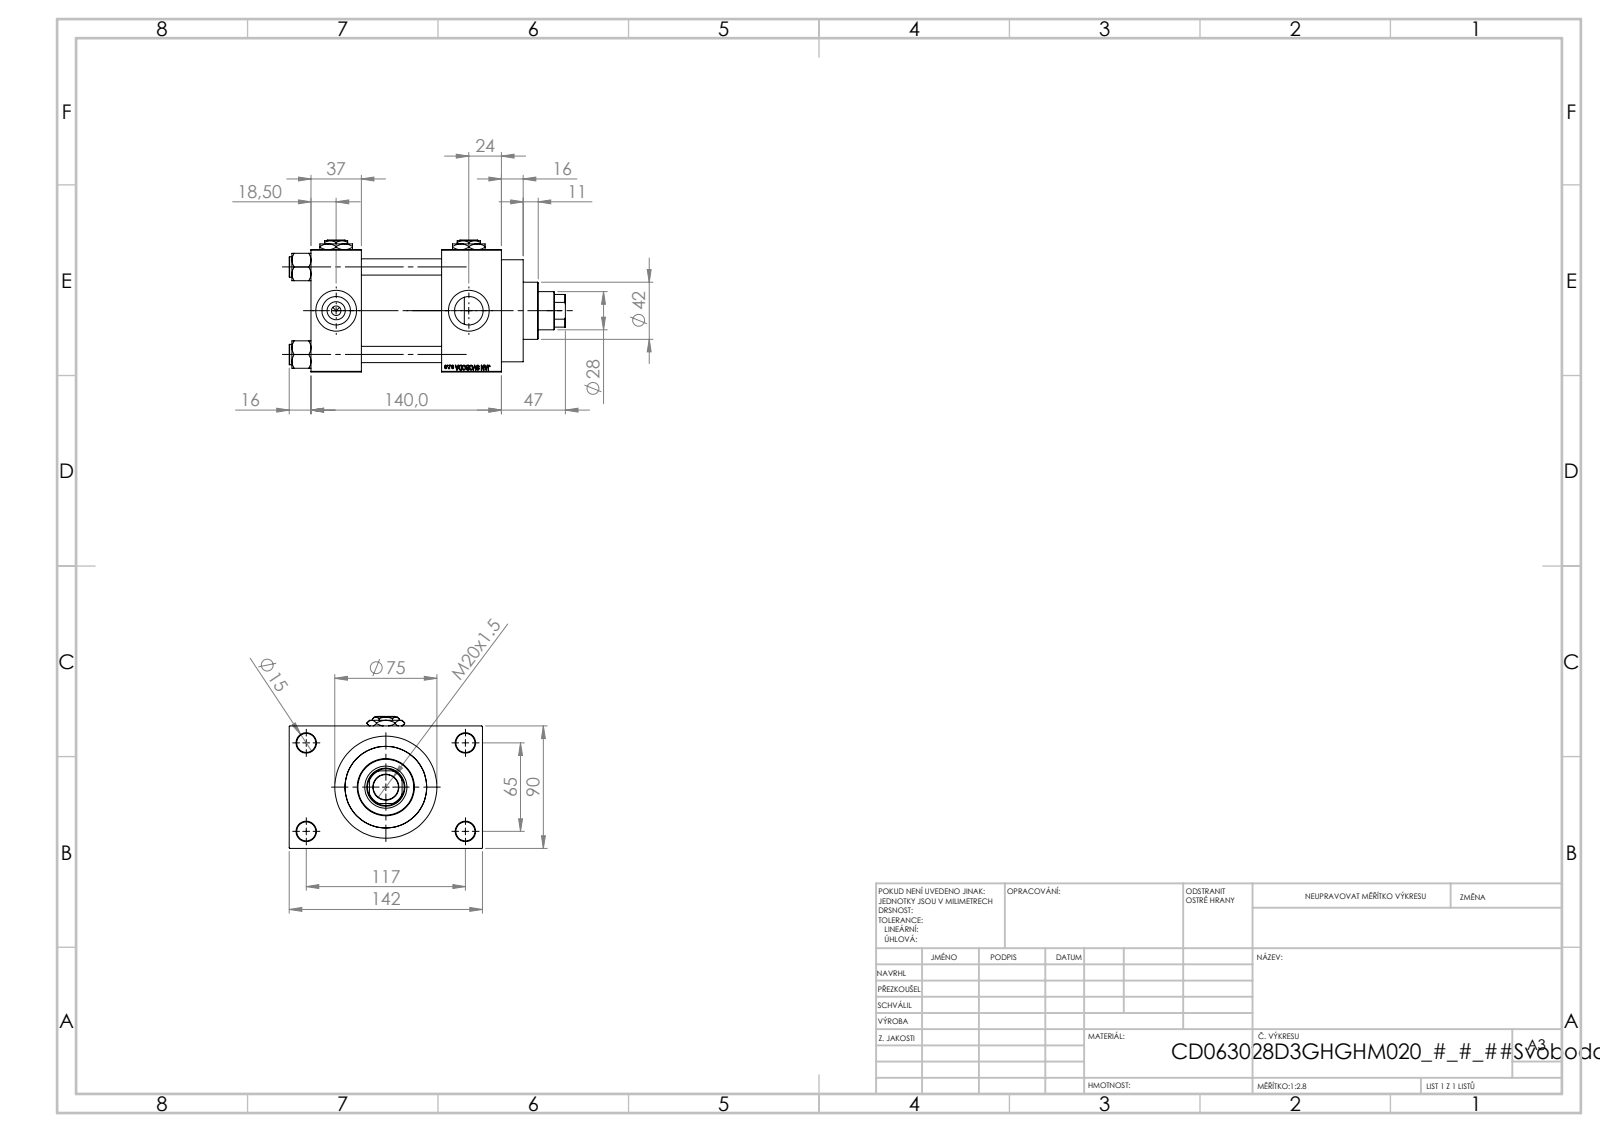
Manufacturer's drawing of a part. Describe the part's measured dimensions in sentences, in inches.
The part is named "V215CD_VC_A; V215CD_D_TYCINKA; Zatka_pro_OIL_PORT; V215CD_NUT_M5_D (+2 more)". Its 3-D file was written by "SolidWorks 2019 (CONFIG_CONTROL_DESIGN)". It is 13 solids with 1204 faces: 545 planar, 99 cylindrical and 560 other. Overall it measures 7.992 by 5.591 by 3.819 inches. Its volume is 66.58 cubic inches and its surface area 317.7 square inches. Round holes: 4 of diameter 0.472, 4 of diameter 0.551, 4 of diameter 0.825, 4 of diameter 1.181, 3 of diameter 0.276, 1 of diameter 0.728, 1 of diameter 1.102, 1 of diameter 1.22, 1 of diameter 1.969, 1 of diameter 2.362, 1 of diameter 2.48. Round bosses or shafts: 4 of diameter 0.591, 1 of diameter 2.953, 1 of diameter 2.717, 1 of diameter 1.654. Partial cylindrical surfaces (rounded edges, fillets, slot ends): 1 of radius 0.531. The main face-to-face distances are 3.543, 2.323, 1.457, 3.78, 5.512, 4.055, 1.732, 1.024, 4.567, 0.63. The hole center spacings are 1.037, 1.79, 2.531, 2.635, 2.748, 3.569, 4.383, 2.559.
